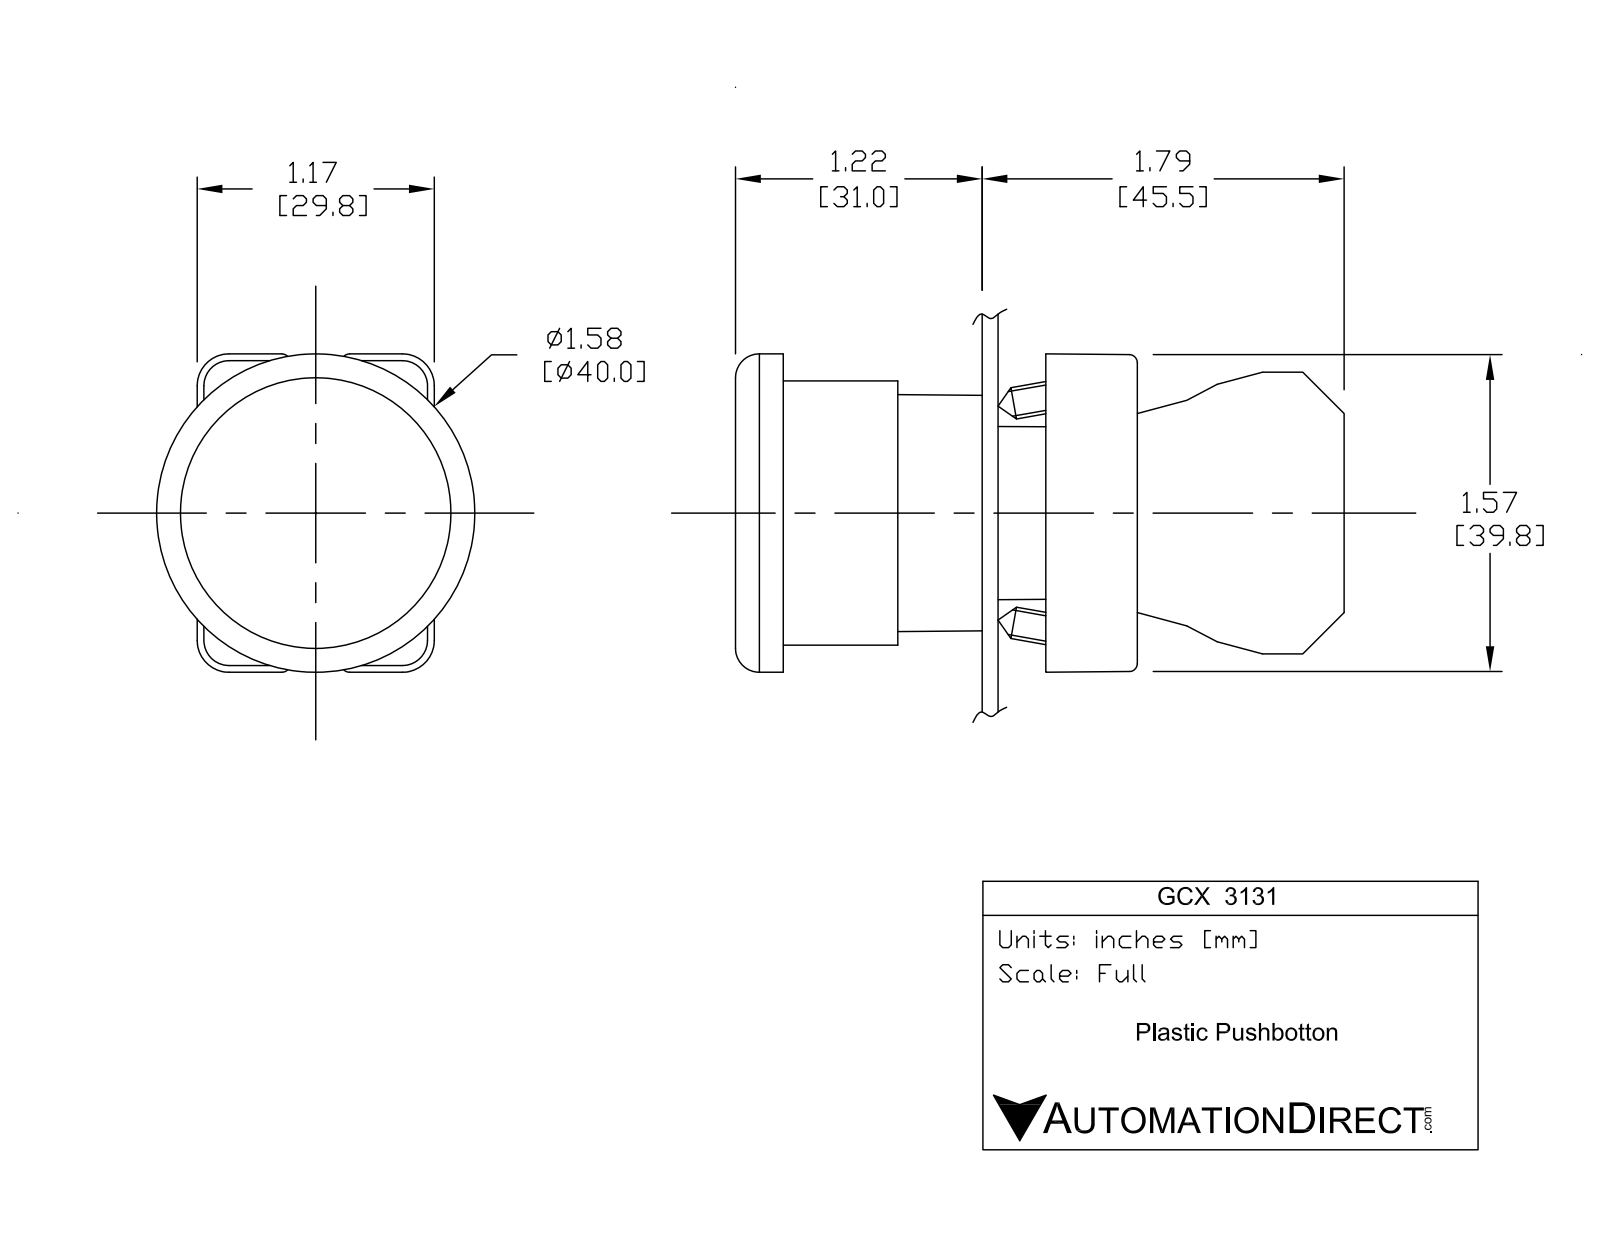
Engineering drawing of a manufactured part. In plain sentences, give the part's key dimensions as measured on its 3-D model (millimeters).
The part is named "GCX3131; ecx1030; ECX3029-2; GCX313X OPERATOR". Its 3-D file was written by "SolidWorks 2016 (AUTOMOTIVE_DESIGN)". It is 6 solids with 389 faces: 224 planar, 134 cylindrical and 31 other. Overall it measures 74.8 by 40.2 by 40 millimeters. Its volume is 29 940 cubic millimeters and its surface area 21 550 square millimeters. Round holes: 2 of diameter 2, 2 of diameter 3.1, 2 of diameter 3.3, 1 of diameter 2.2, 1 of diameter 5, 1 of diameter 22.3, 1 of diameter 22.6, 1 of diameter 26, 1 of diameter 30. Round bosses or shafts: 2 of diameter 4, 1 of diameter 33, 1 of diameter 29.8, 1 of diameter 24, 1 of diameter 21.7, 1 of diameter 19.8. Partial cylindrical surfaces (rounded edges, fillets, slot ends): 24 of radius 1.5, 12 of radius 1, 12 of radius 3.1, 12 of radius 4, 4 of radius 1, 2 of radius 3.3, 1 of radius 0.5, 1 of radius 1.6. The main face-to-face distances are 48.8, 14.7, 0.8, 44.8, 4, 0.8, 18.3, 26.5, 30.5, 17.5. The hole center spacings are 6, 13.8, 12, 12.4.
